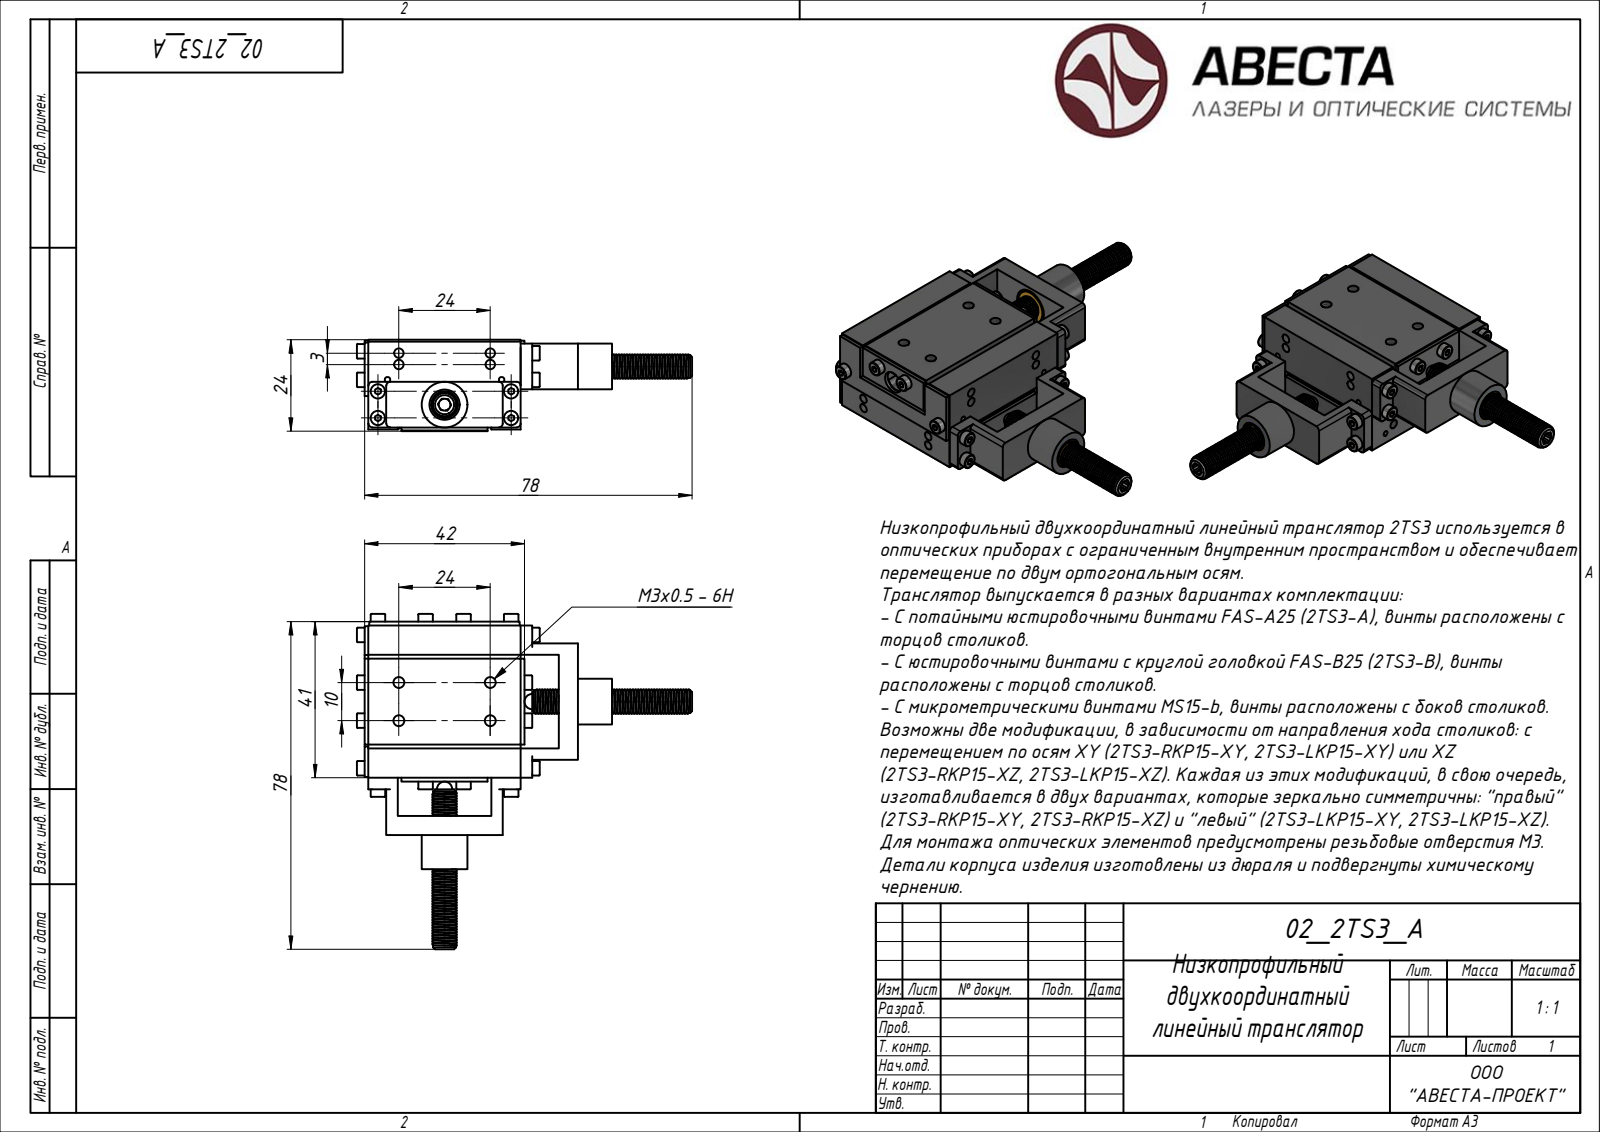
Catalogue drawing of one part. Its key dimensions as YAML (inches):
step_written_by: "ST-DEVELOPER v15 (AUTOMOTIVE_DESIGN)"
units: inches
bodies: {solids: 19, faces: 878, planar: 0, cylindrical: 0, other: 878}
overall_size: [3.493, 3.465, 0.945]
